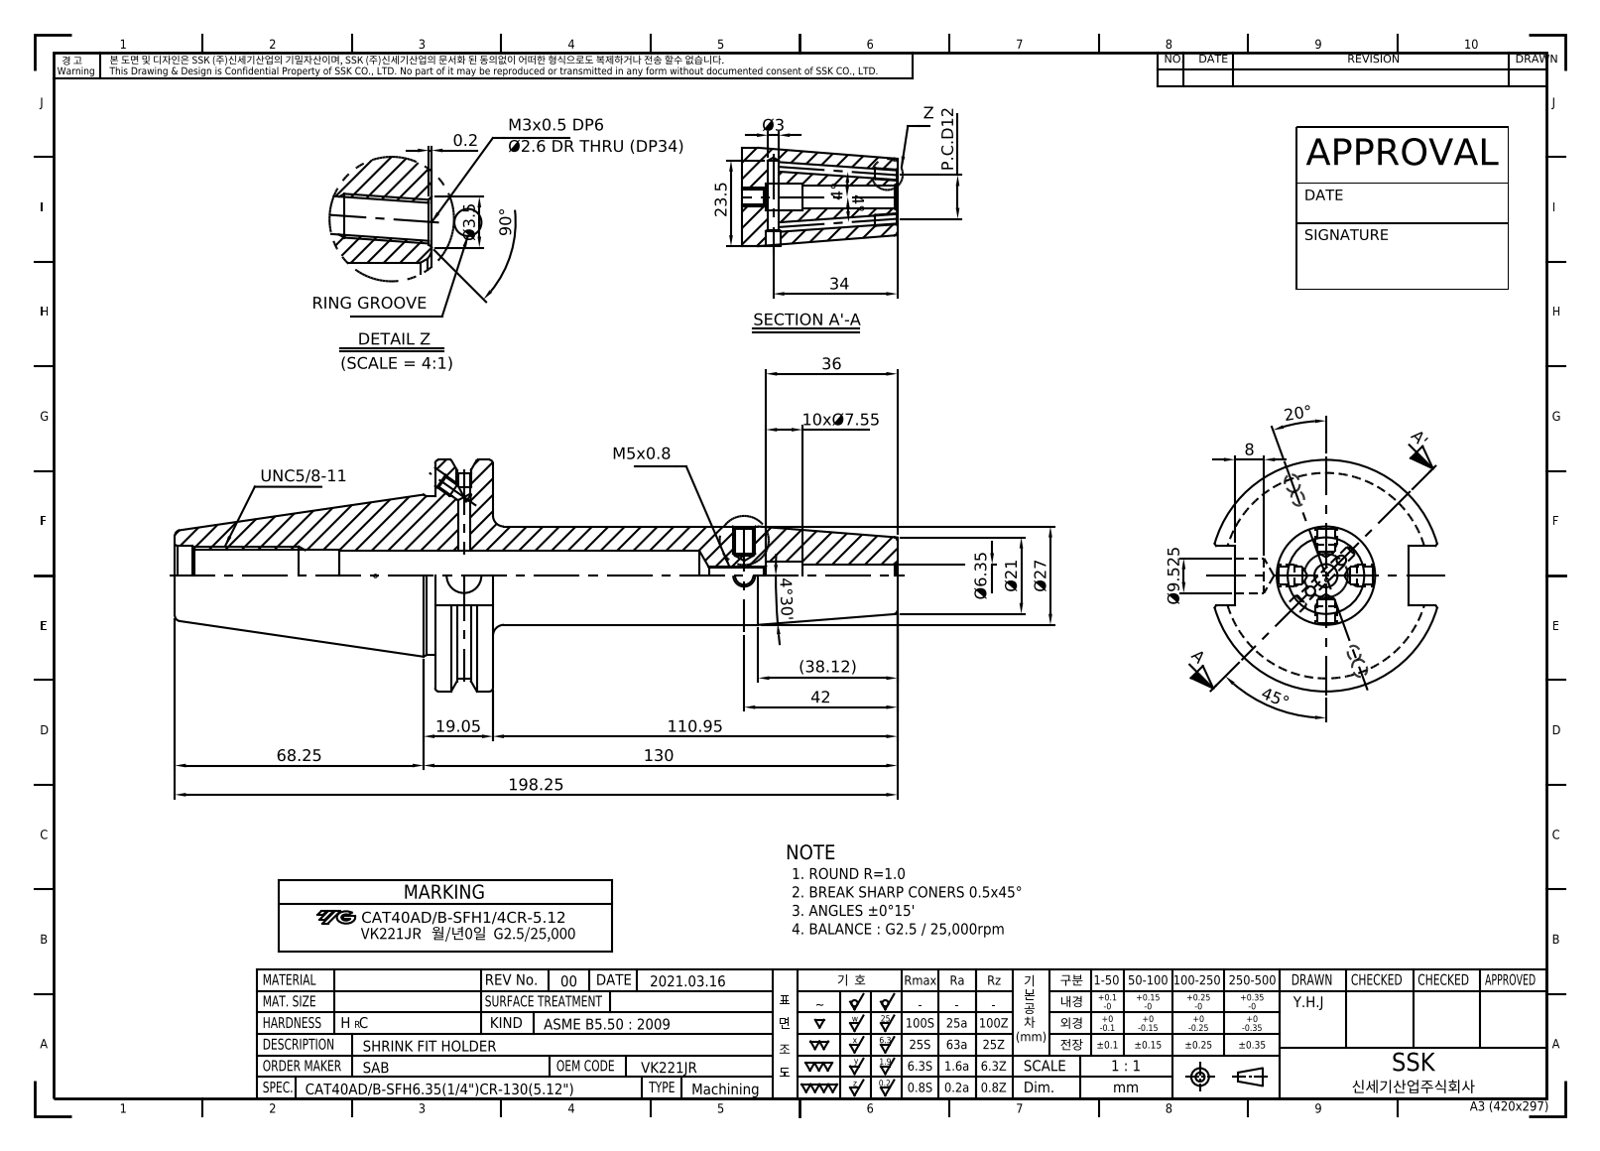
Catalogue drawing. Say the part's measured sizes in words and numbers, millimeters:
The part is named "LO-CAT40ADB-SFH6.35CR-130". Its 3-D file was written by "Autodesk Inventor 2022 (AUTOMOTIVE_DESIGN)". It is 1 solid with 91 faces: 37 planar, 31 cylindrical and 23 other. Overall it measures 198.25 by 63.5 by 61.09 millimeters. Its volume is 150 450 cubic millimeters and its surface area 33 436 square millimeters. Round holes: 4 of diameter 3.24, 2 of diameter 2.46, 2 of diameter 4, 2 of diameter 4.2, 1 of diameter 4.3, 1 of diameter 6.35, 1 of diameter 7.55, 1 of diameter 9.53, 1 of diameter 13, 1 of diameter 13.39, 1 of diameter 16.3. Round bosses or shafts: 1 of diameter 63.5, 1 of diameter 43.6, 1 of diameter 27. Partial cylindrical surfaces (rounded edges, fillets, slot ends): 1 of radius 28.15. The main face-to-face distances are 15.88, 126.83, 110.95, 47.6, 16.38, 71.42, 87.3, 198.25, 77.47, 6.05.
